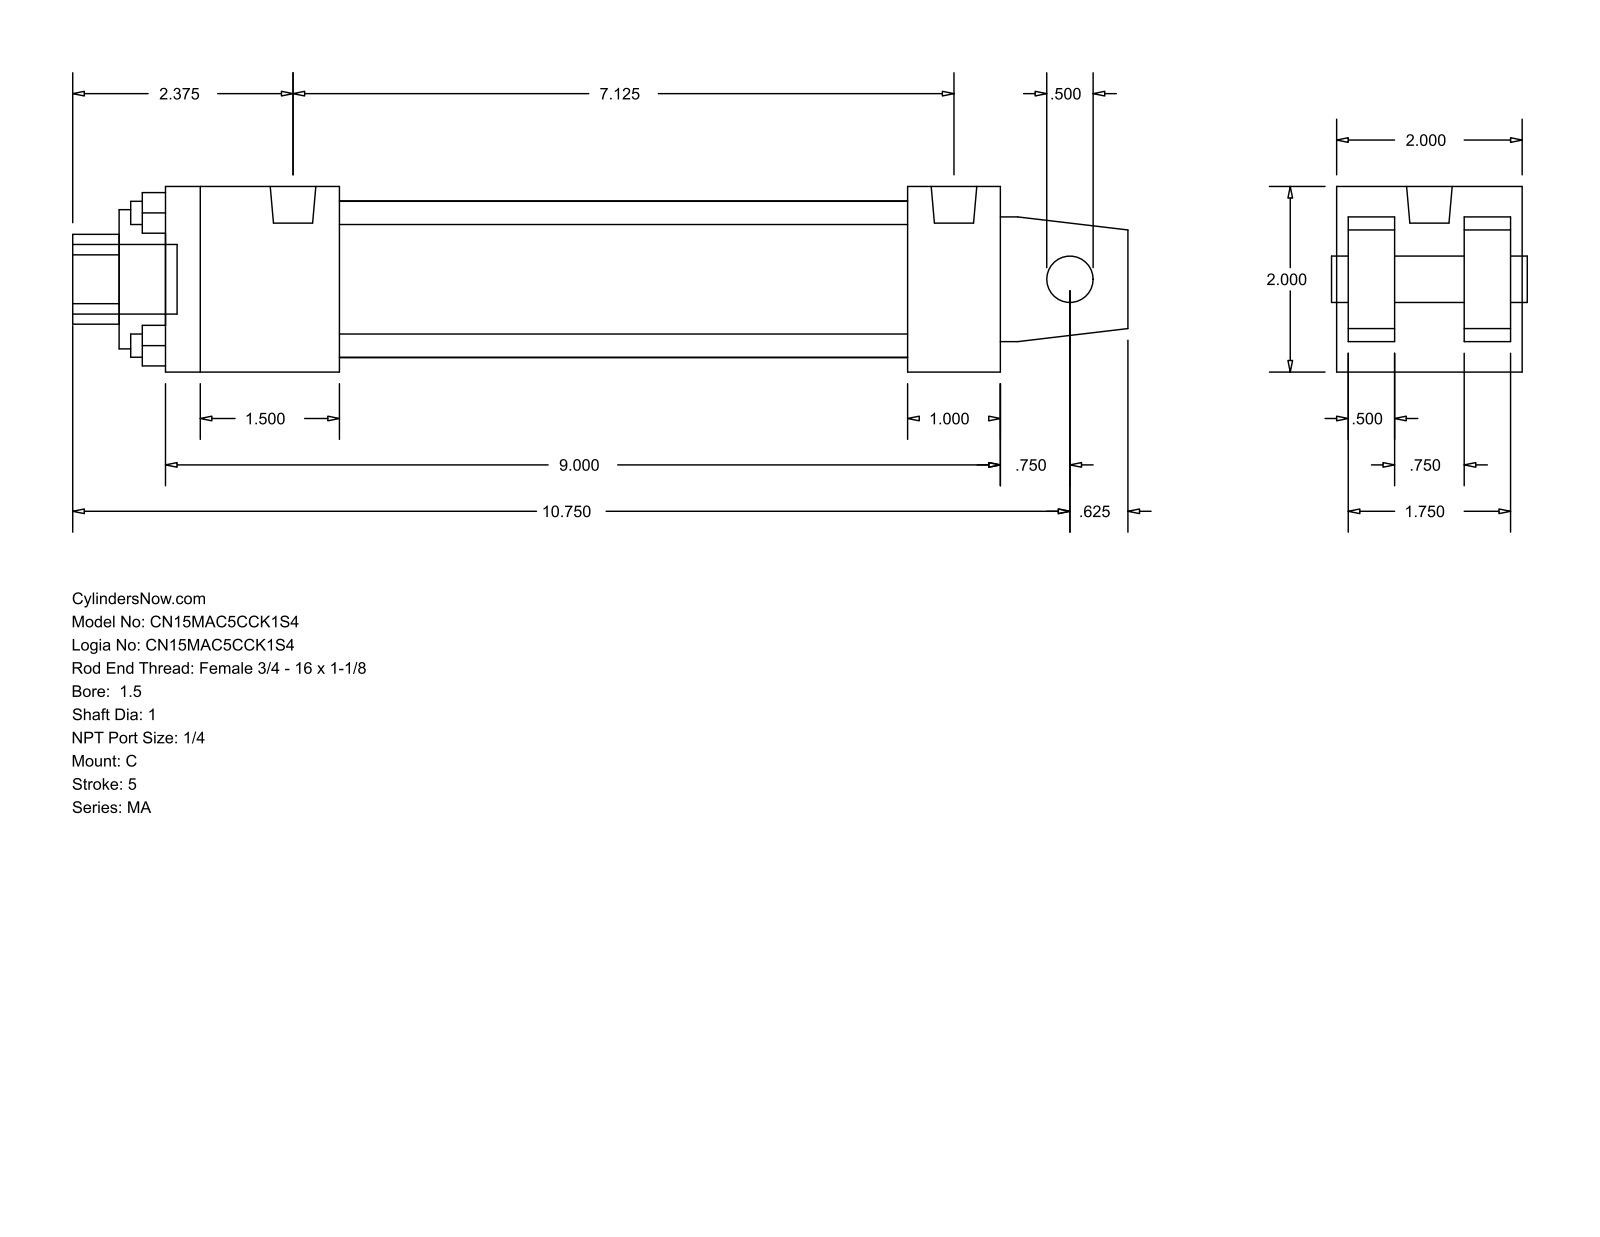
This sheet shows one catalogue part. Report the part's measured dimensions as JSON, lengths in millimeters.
{"part_name": "MA_C__0150_1", "step_written_by": "GSSL Pune (CONFIG_CONTROL_DESIGN)", "units": "millimeters", "bodies": {"solids": 0, "faces": 103, "planar": 76, "cylindrical": 27, "other": 0}, "overall_size": [288.93, 50.8, 50.8], "round_holes": [[6.35, 4], [12.7, 1], [25.4, 1], [38.1, 1], [42.93, 1]], "round_bosses_or_shafts": [[7.94, 4], [12.49, 2], [19.05, 1]], "partial_cylinders_radius": [[12.29, 1]], "face_to_face_distances": [50.8, 47.63, 12.7, 34.93, 3.17, 15.87, 31.76, 60.33, 215.9, 44.46], "hole_center_spacings": [25.68, 36.32, 51.36]}
